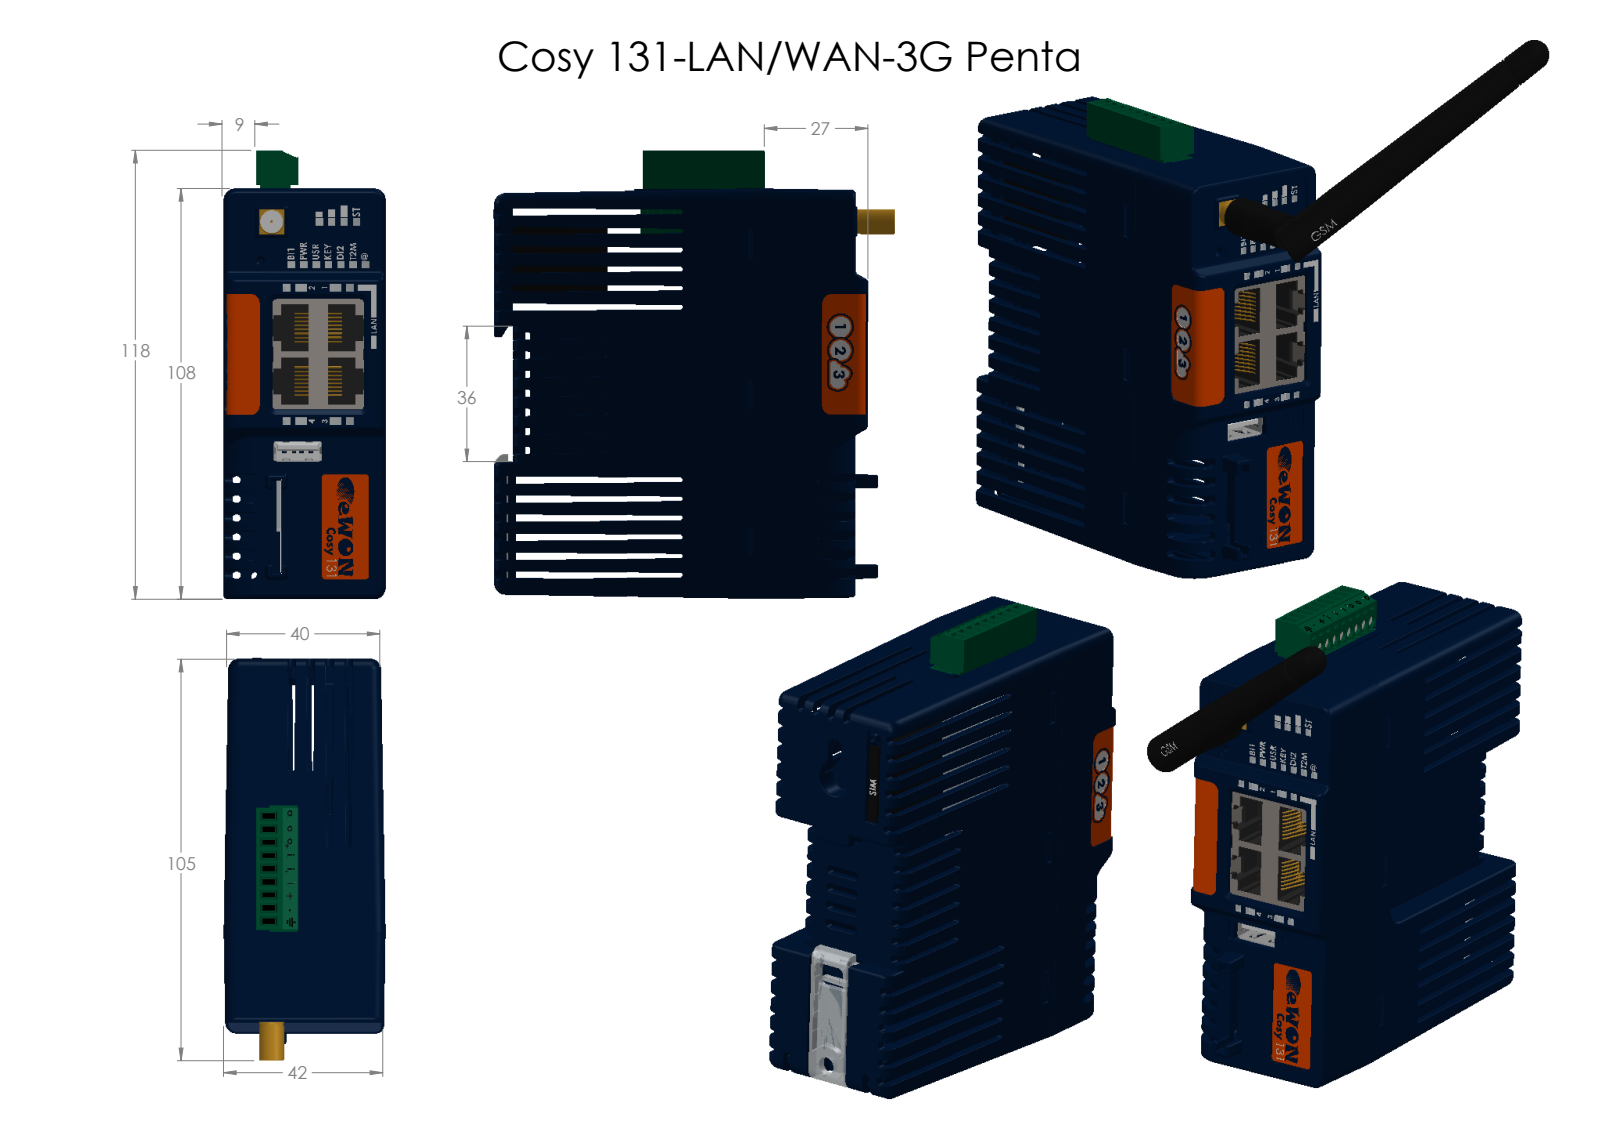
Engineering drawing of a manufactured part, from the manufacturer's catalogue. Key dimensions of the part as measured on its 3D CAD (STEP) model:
Part name (STEP PRODUCT): Cosy 131  LAN_WAN - 3G Penta; DEFAULT-12; DEFAULT-7; DEFAULT-5 (+8 more)
STEP written by: SolidWorks 2015 (AUTOMOTIVE_DESIGN)
Units: millimetres
Bodies: 74 solids, 7188 faces (4207 planar, 1689 cylindrical, 1292 other)
Overall size (bounding box): 154.62 × 148.02 × 75.24
Volume: 93 162 mm³ · Surface area: 130 896 mm²
Round holes (diameter × count): ⌀0.45 ×16, ⌀1 ×16, ⌀0.8 ×9, ⌀2 ×9, ⌀3 ×9, ⌀6 ×2, ⌀0.5 ×1, ⌀1.8 ×1, ⌀4.5 ×1, ⌀5.32 ×1, ⌀5.48 ×1, ⌀6.22 ×1
Round bosses / shafts (diameter × count): ⌀0.45 ×16, ⌀0.5 ×9, ⌀10 ×2, ⌀9.5 ×1, ⌀9.3 ×1, ⌀7.43 ×1, ⌀7.16 ×1, ⌀6.34 ×1
Partial cylindrical surfaces — rounded edges, fillets, slot ends (radius × count): R0.25 ×293, R0.5 ×133, R0.2 ×116, R1 ×80, R0.15 ×74, R0.75 ×30, R0.12 ×24, R0.23 ×24
Main face-to-face distances: 2, 5, 40.6, 7.08, 40.61, 10, 33.53, 3.25, 105.75, 15
Hole centre spacings: 3.5, 2.84, 7, 2.54, 10.5, 14, 5.08, 14.12
